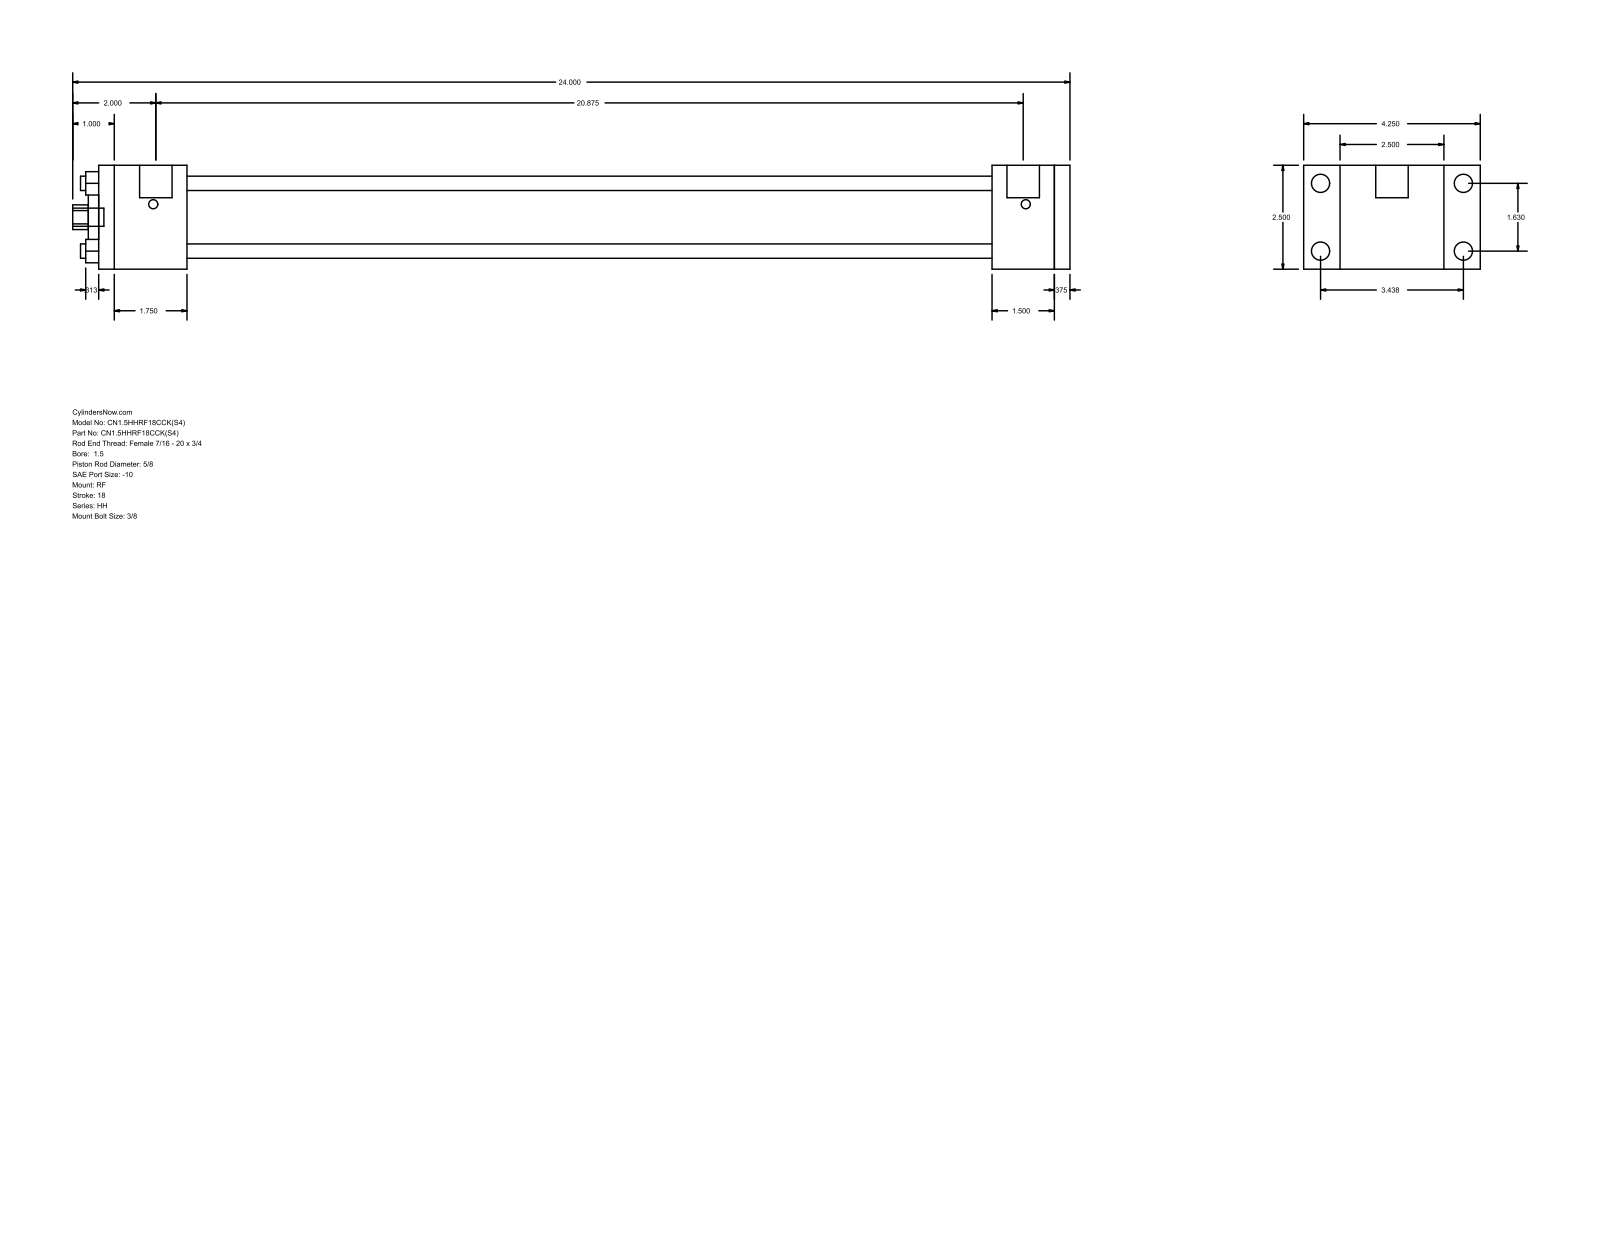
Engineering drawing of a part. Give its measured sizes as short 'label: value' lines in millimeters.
name: HH_RF__0150_0.625
written by: GSSL Pune (CONFIG_CONTROL_DESIGN)
unit: mm
bodies: 0 solids, 92 faces (64 planar, 28 cylindrical, 0 other)
size: 609.6 × 107.95 × 63.5
holes: 4× ⌀8.76, 1× ⌀15.88, 1× ⌀28.57, 1× ⌀44.45
bosses: 4× ⌀11.13, 4× ⌀5.56, 2× ⌀19.84, 1× ⌀11.11
rounds: 1× R7.54
face distances: 63.5, 593.72, 9.52, 38.1, 584.2, 53.97, 546.1, 492.13, 530.23, 539.75
hole spacings: 29.27, 41.4, 58.55
